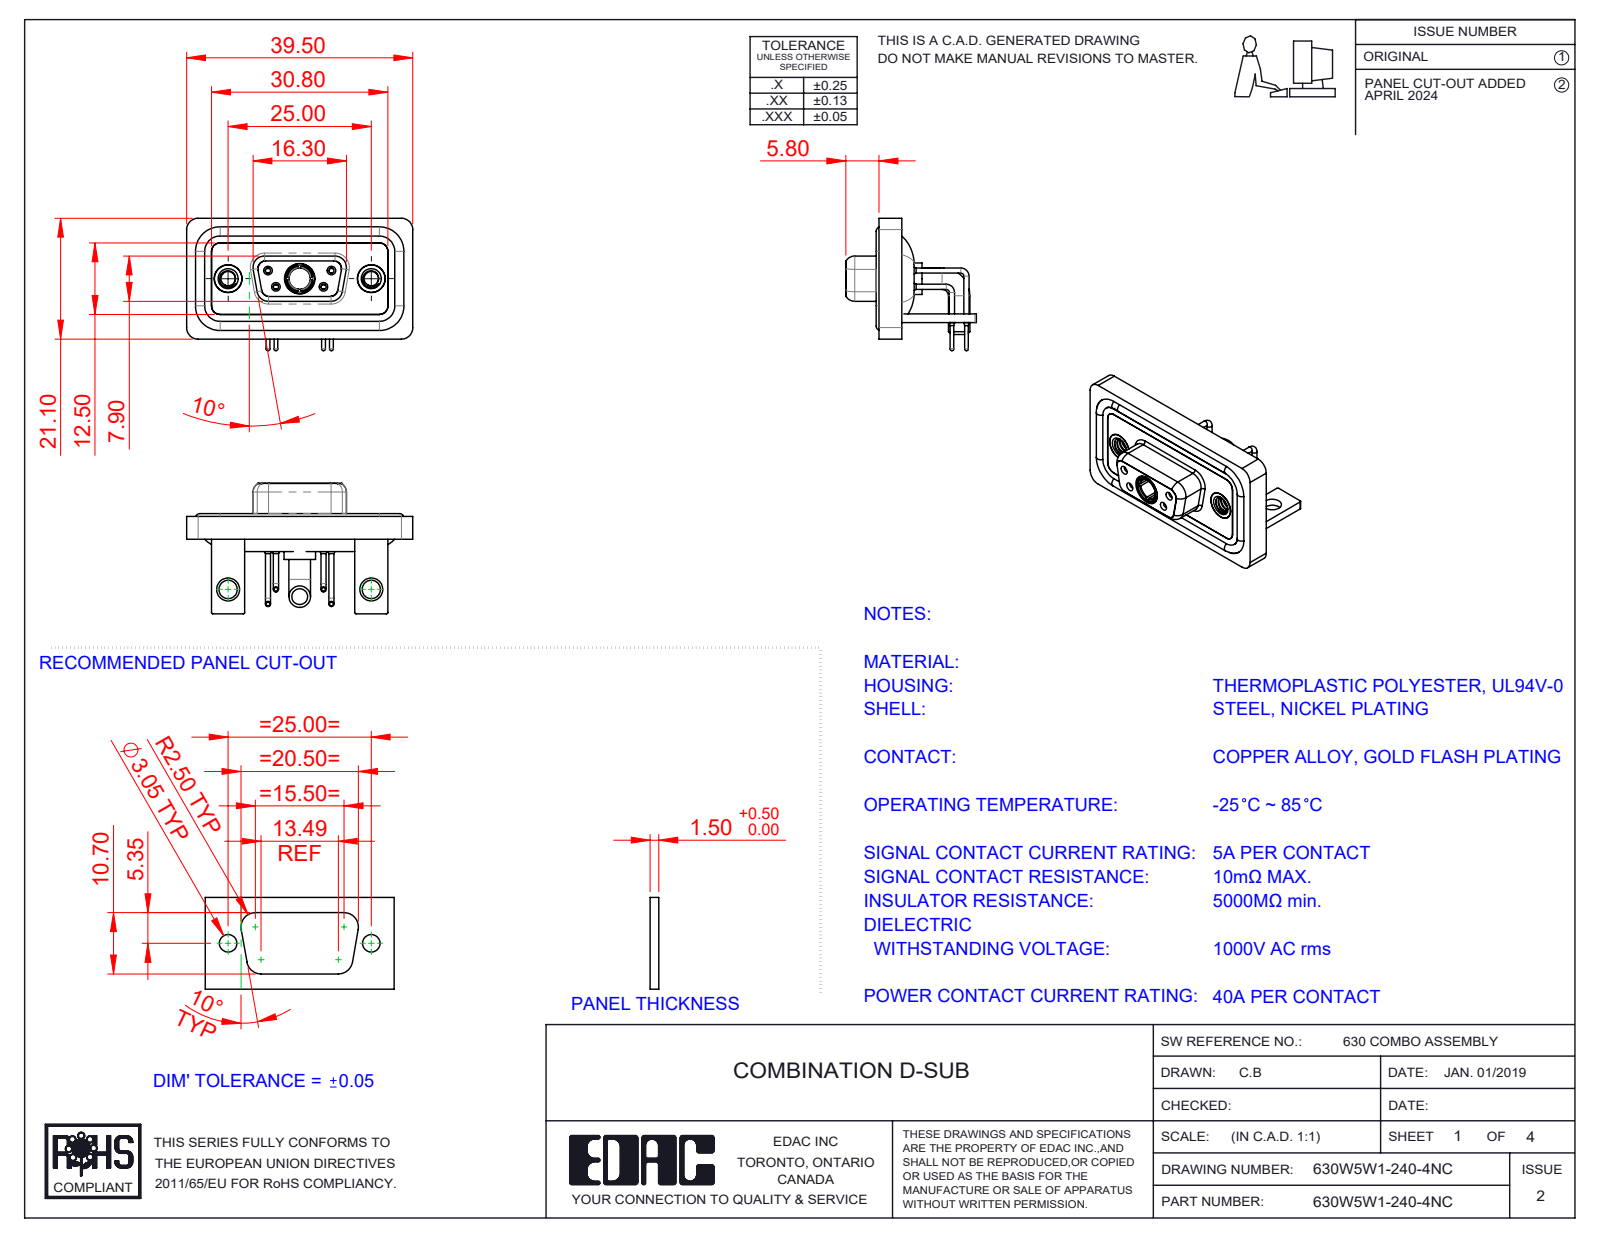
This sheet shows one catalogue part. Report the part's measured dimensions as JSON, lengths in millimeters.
{"part_name": "630Combo Threaded Rivet_A; 630Combo Shell Rear_09 Contacts; 630Combo Contact Row 1_50 Contacts; 630Combo Shell Front_09 Contacts (+6 more)", "step_written_by": "SolidWorks 2023 (CONFIG_CONTROL_DESIGN)", "units": "millimeters", "bodies": {"solids": 15, "faces": 718, "planar": 214, "cylindrical": 327, "other": 177}, "overall_size": [39.5, 23.12, 22.8], "volume_mm3": 5261, "surface_area_mm2": 8626, "round_holes": [[0.9, 4], [1.1, 4], [1.5, 4], [2, 4], [4.85, 3], [1.6, 2], [1.7, 2], [2.5, 2], [3.2, 2], [4, 2], [4.05, 2], [5, 2]], "round_bosses_or_shafts": [[1.6, 6], [0.9, 4], [0.65, 4], [4.95, 2], [4.8, 2], [3.75, 2], [5.5, 1], [5.2, 1]], "partial_cylinders_radius": [[2, 19], [1.5, 18], [0.25, 16], [1.35, 8], [1.6, 8], [0.5, 5], [0.6, 4], [0.65, 4]], "face_to_face_distances": [0.4, 2.9, 1.5, 1.8, 1.1, 3.7, 1.6, 0.8, 2.5, 3.1], "hole_center_spacings": [3.16, 5.72, 7.1, 12.5, 18.1, 25, 4.39, 4.4]}
